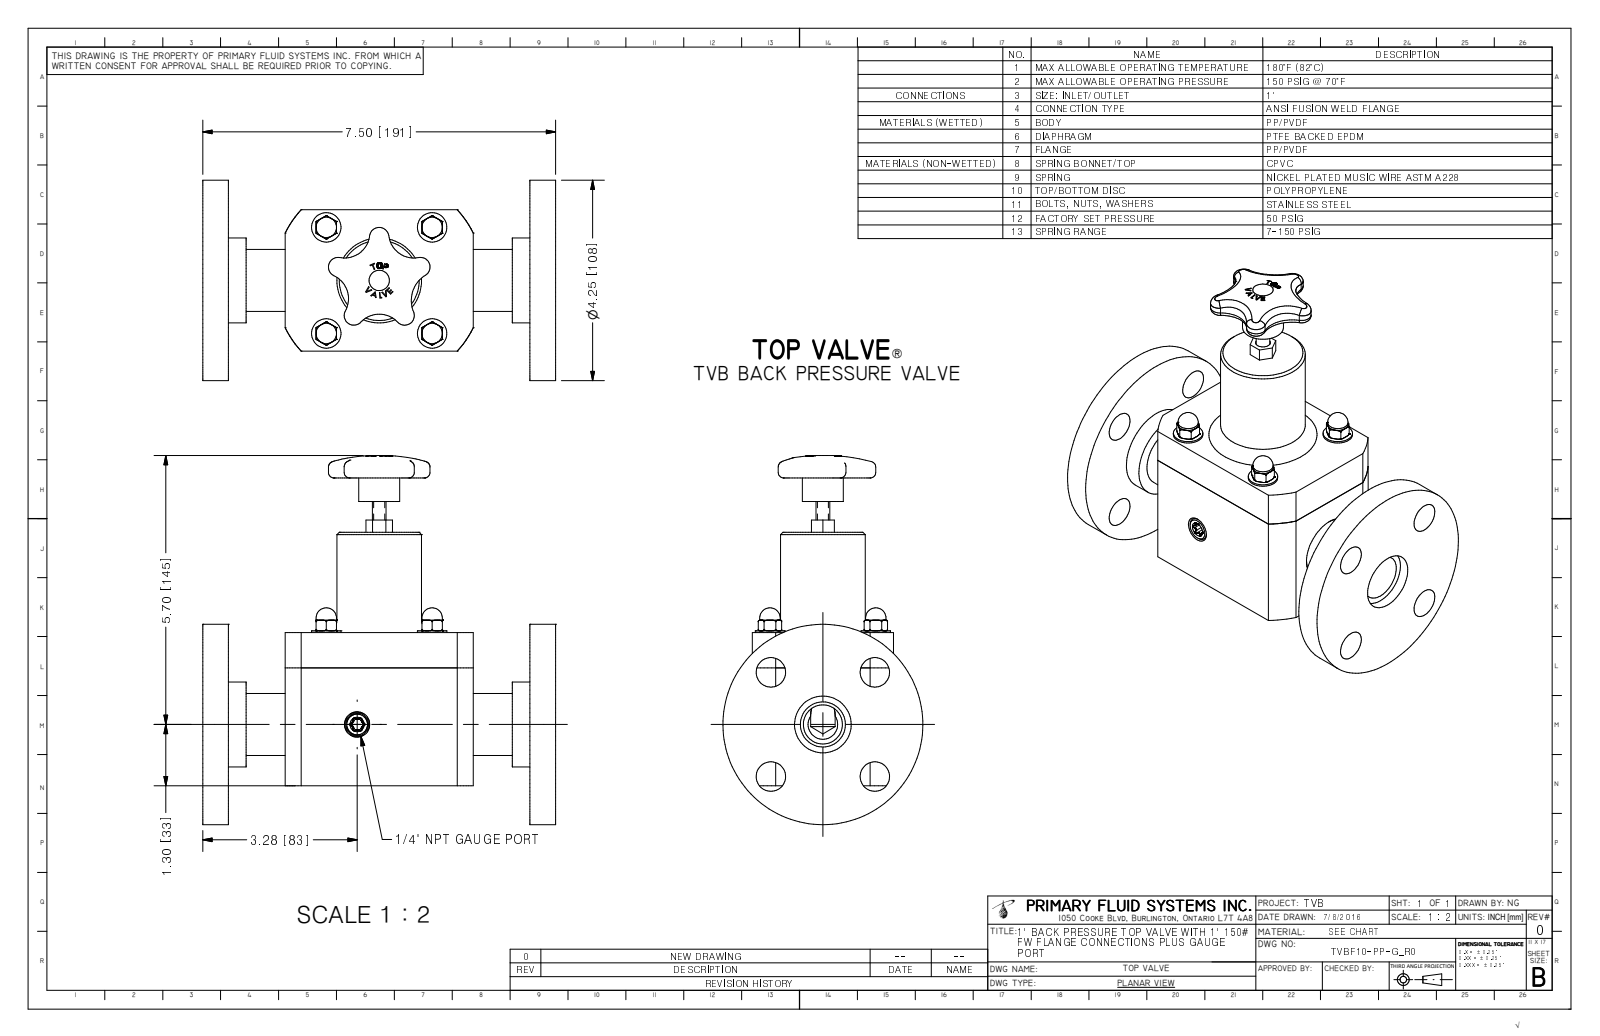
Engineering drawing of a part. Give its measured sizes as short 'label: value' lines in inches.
name: TVBF10-PP-G_R0
written by: Autodesk Inventor 2009 (AUTOMOTIVE_DESIGN)
unit: in
bodies: 1 solid, 391 faces (164 planar, 71 cylindrical, 156 other)
size: 7.827 × 7.5 × 4.25
volume: 59.37 in³; area: 190.3 in²
holes: 4× ⌀0.175, 4× ⌀0.625, 1× ⌀0.957, 1× ⌀1.205
bosses: 4× ⌀0.625, 4× ⌀0.433, 4× ⌀0.375, 2× ⌀1.8, 1× ⌀4.25, 1× ⌀1.315, 1× ⌀0.87, 1× ⌀0.293
rounds: 6× R0.027, 5× R0.085, 5× R0.205, 4× R0.536, 4× R0.656, 1× R0.625, 1× R0.745, 1× R2.238
face distances: 0.545, 6.955, 7.5, 3, 6.41, 1.75, 5.75, 1.205, 5.205, 3.25
hole spacings: 1.562, 2.209, 2.25, 3.125, 3.182
